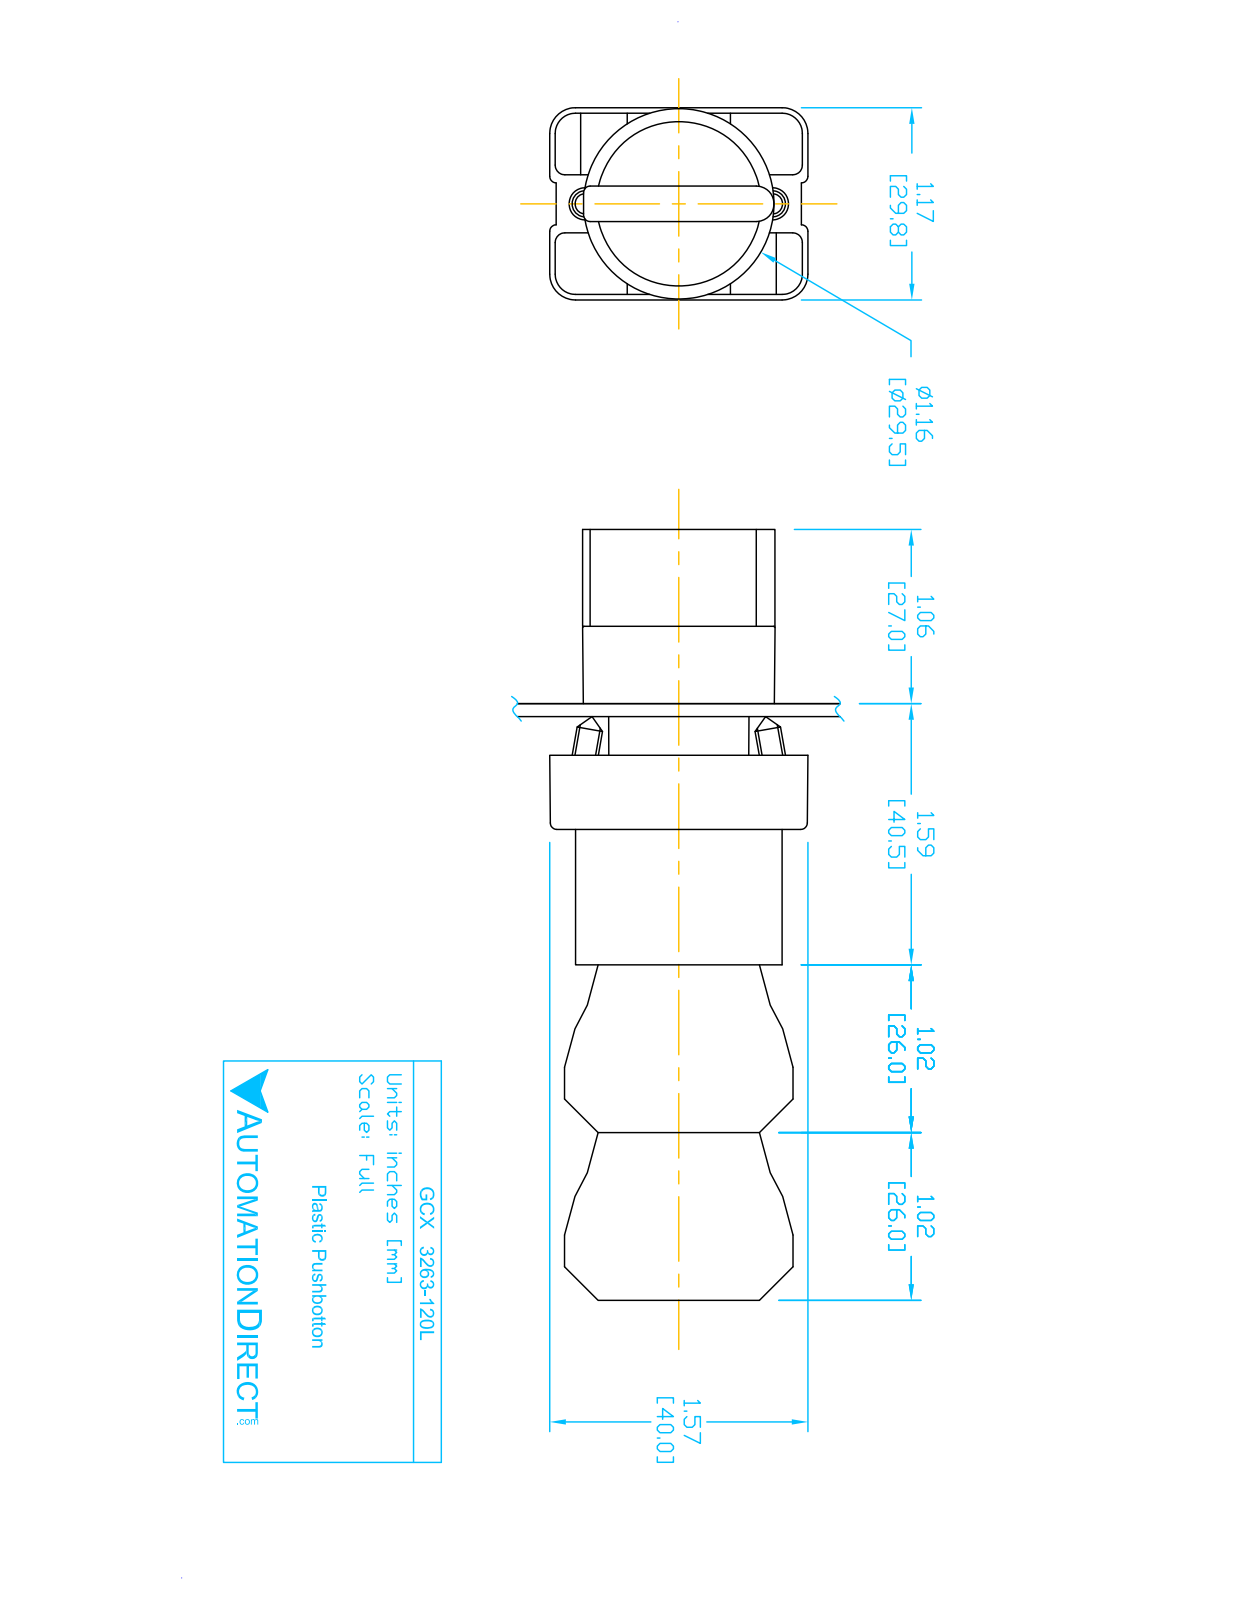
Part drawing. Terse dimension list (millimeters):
name: GCX3263L OPERATOR; ECX1050; GCX3263-120L; ECX3029-2 (+2 more)
written by: SolidWorks 2016 (AUTOMOTIVE_DESIGN)
unit: mm
bodies: 11 solids, 724 faces (488 planar, 193 cylindrical, 43 other)
size: 118.8 × 40.2 × 29.9
volume: 77 850 mm³; area: 38 210 mm²
holes: 4× ⌀2, 2× ⌀2.2, 2× ⌀3.1, 2× ⌀3.3, 1× ⌀5, 1× ⌀11.9, 1× ⌀22.3, 1× ⌀22.6, 1× ⌀26
bosses: 4× ⌀4, 1× ⌀29.8, 1× ⌀25.5, 1× ⌀24, 1× ⌀21.7, 1× ⌀19.8, 1× ⌀12.8
rounds: 24× R1.5, 12× R1, 12× R3.1, 12× R4, 9× R1, 2× R0.5, 2× R1.6, 2× R2
face distances: 14.7, 15.1, 26, 29.7, 0.4, 21, 47, 77.3, 51.3, 30.3
hole spacings: 6, 25.5, 24.7, 12, 13.7, 13.8, 27.5, 12.3
